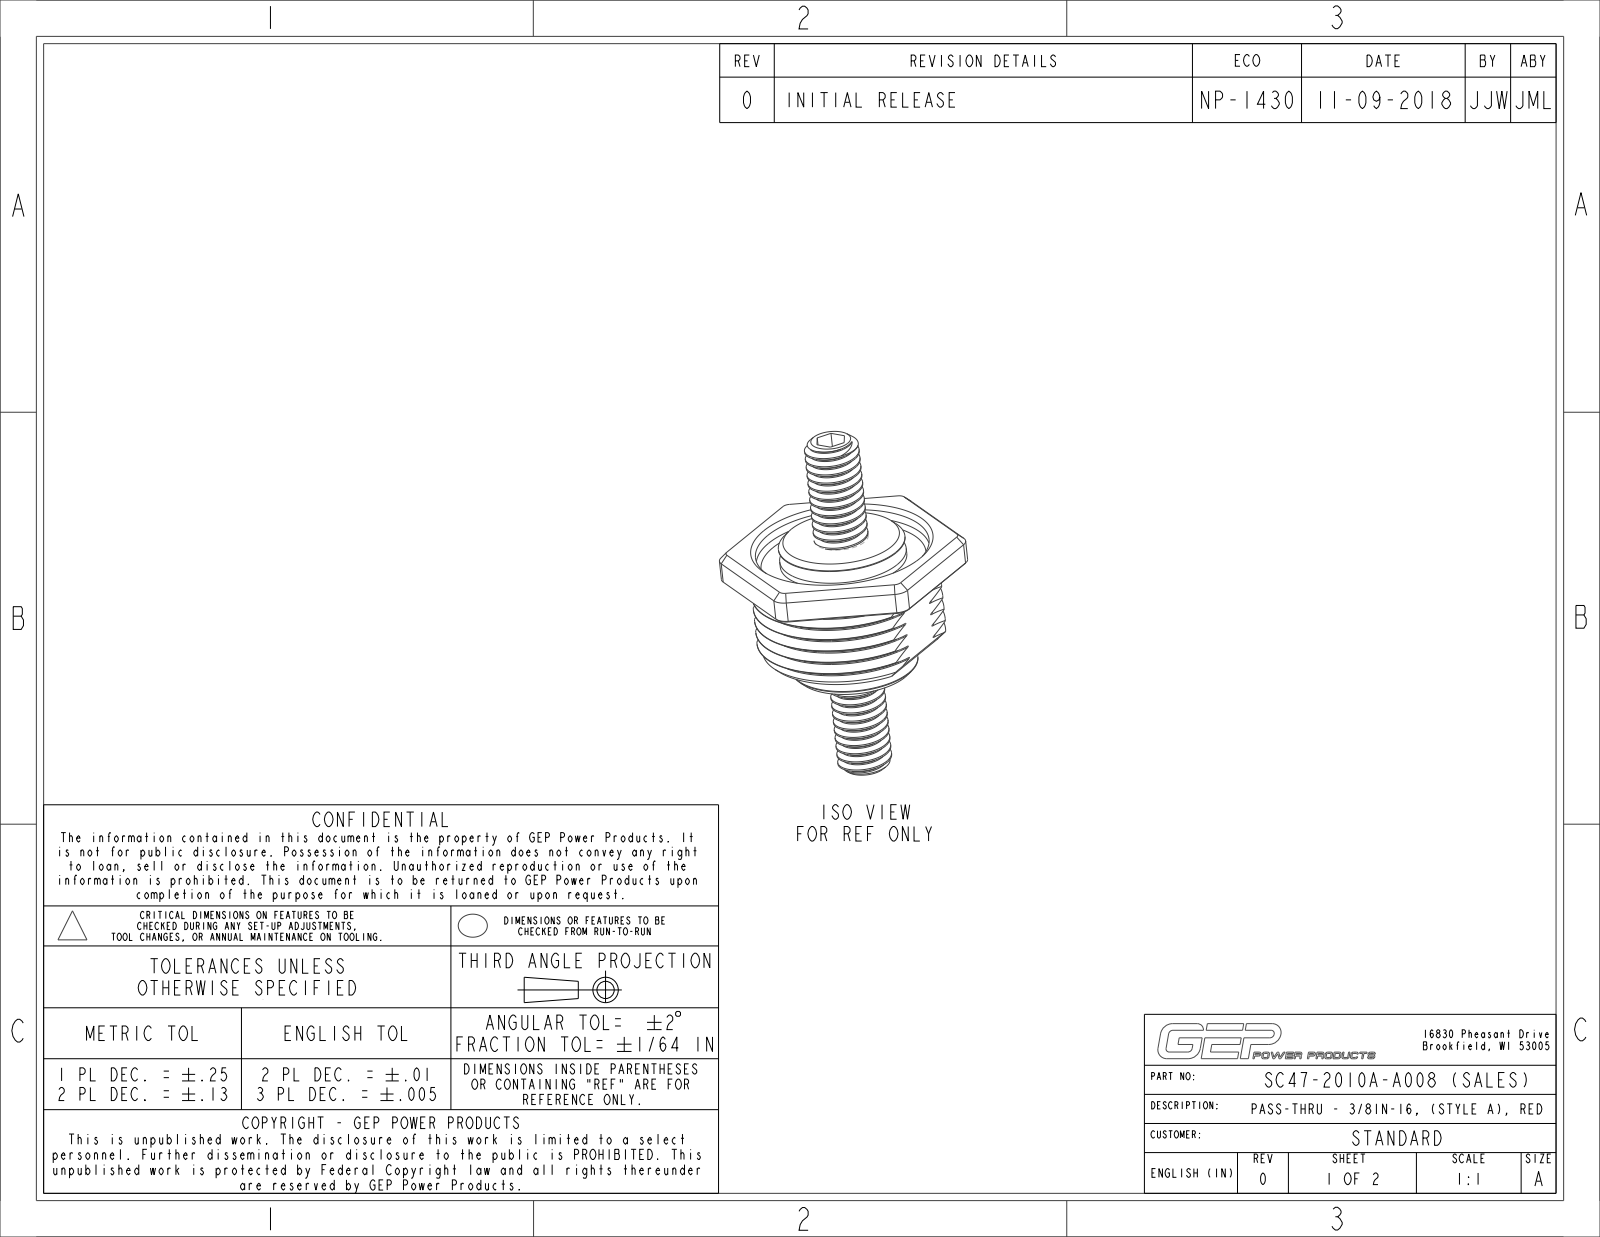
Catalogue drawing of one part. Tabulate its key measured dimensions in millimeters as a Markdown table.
| quantity | value |
| --- | --- |
| part name | SC47-2010A-A008_NCF_SW0001 |
| STEP written by | CREO PARAMETRIC BY PTC INC, 2017110 (CONFIG_CONTROL_DESIGN) |
| units | millimeters |
| bodies | 1 solid, 278 faces (47 planar, 93 cylindrical, 138 other) |
| overall size | 63.5 × 43.21 × 38.1 |
| volume | 19 893 mm³ |
| surface area | 9 134 mm² |
| round holes (diameter × count) | 7.94 × 1, 30.48 × 1 |
| round bosses / shafts (diameter × count) | 22.23 × 1, 9.53 × 1 |
| partial cylindrical surfaces (radius × count) | 2.54 × 6, 0.76 × 2, 16.57 × 1 |
| main face-to-face distances | 4.32, 21.08, 6.35, 1.27, 19.05, 5.08, 25.4, 14.73, 19.81, 16.76 |
